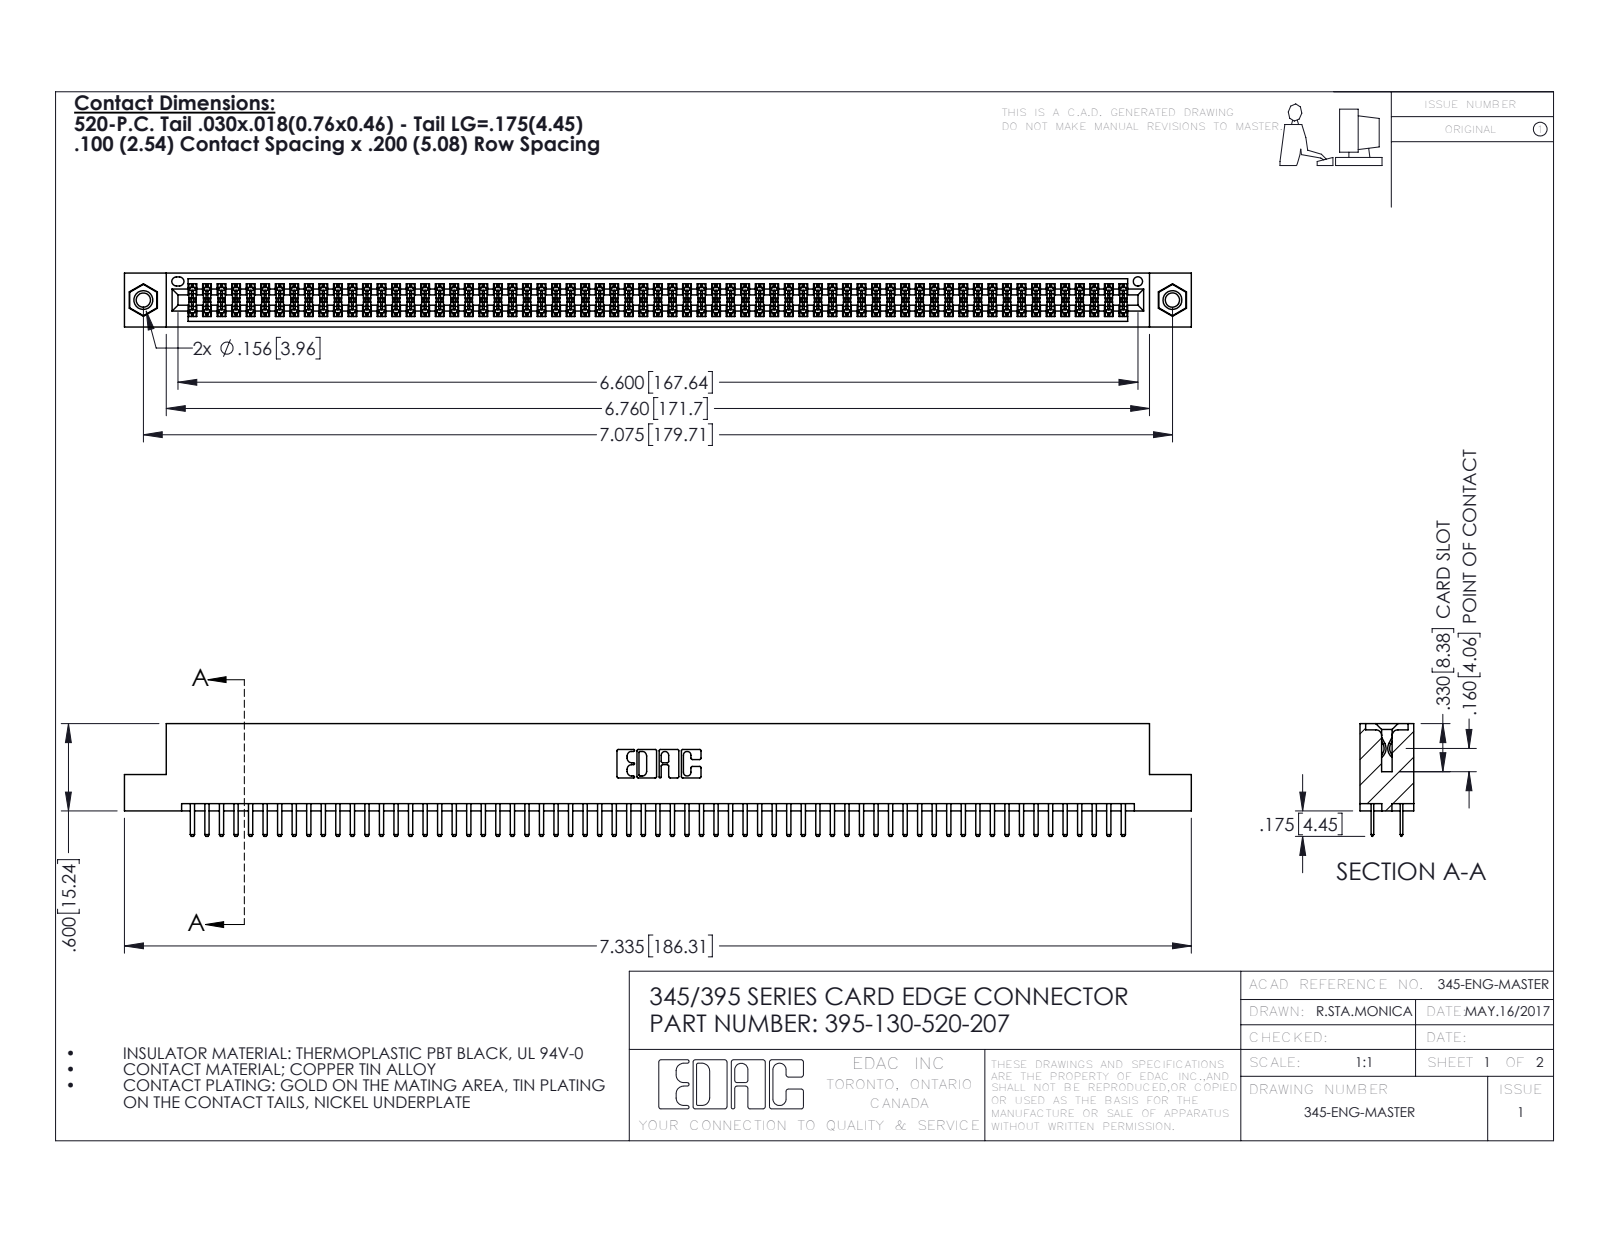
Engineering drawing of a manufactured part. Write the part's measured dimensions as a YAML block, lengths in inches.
part_name: "395-130-520-207; 345 Part_Flush Mounting Lugs - 0.156 Dia-TI; 345-250-001_345-250-005-103; 345-292-001_345-293-120"
step_written_by: "SolidWorks 2016 (CONFIG_CONTROL_DESIGN)"
units: inches
bodies: {solids: 133, faces: 7206, planar: 4662, cylindrical: 2528, other: 16}
overall_size: [7.335, 0.775, 0.37]
volume: 1.113
surface_area: 42.34
round_holes:
  - {diameter: 0.098, count: 2}
  - {diameter: 0.125, count: 2}
  - {diameter: 0.156, count: 2}
  - {diameter: 0.064, count: 1}
round_bosses_or_shafts:
  - {diameter: 0.155, count: 2}
partial_cylinders:
  - {radius: 0.006, count: 195}
  - {radius: 0.01, count: 134}
  - {radius: 0.01, count: 22}
  - {radius: 0.007, count: 6}
  - {radius: 0.031, count: 6}
  - {radius: 0.026, count: 3}
  - {radius: 0.014, count: 2}
  - {radius: 0.019, count: 2}
face_to_face_distances: [0.072, 0.298, 0.2, 0.37, 0.098, 0.272, 0.025, 0.225, 0.022, 0.072]
hole_center_spacings: [0.27, 6.839, 7.075]
